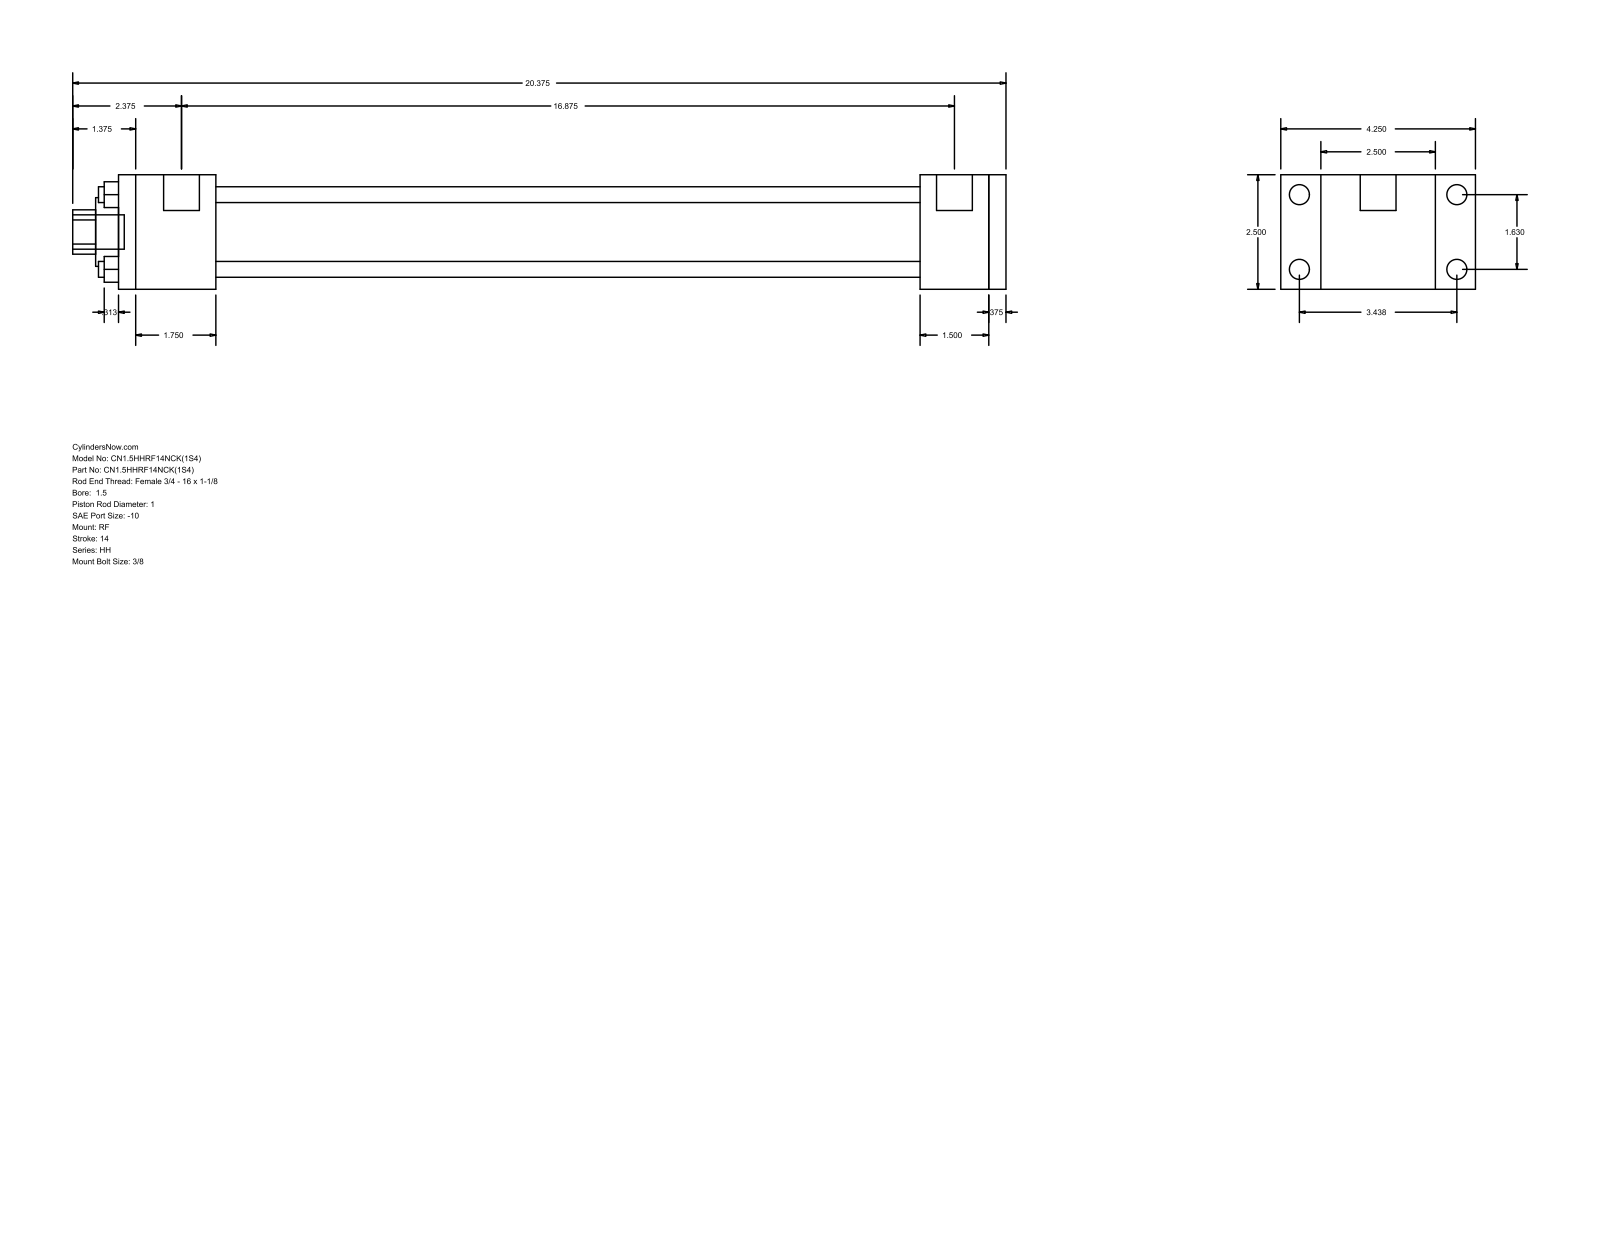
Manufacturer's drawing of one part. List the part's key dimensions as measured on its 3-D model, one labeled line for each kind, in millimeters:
Part name (STEP PRODUCT): HH_RF__0150_1
STEP written by: GSSL Pune (CONFIG_CONTROL_DESIGN)
Units: millimetres
Bodies: 0 solids, 92 faces (64 planar, 28 cylindrical, 0 other)
Overall size (bounding box): 517.52 × 107.95 × 63.5
Round holes (diameter × count): ⌀8.76 ×4, ⌀25.4 ×1, ⌀38.1 ×1, ⌀44.45 ×1
Round bosses / shafts (diameter × count): ⌀11.13 ×4, ⌀5.56 ×4, ⌀19.84 ×2, ⌀19.05 ×1
Partial cylindrical surfaces — rounded edges, fillets, slot ends (radius × count): R12.29 ×1
Main face-to-face distances: 63.5, 9.52, 390.52, 428.62, 438.14, 38.1, 47.62, 53.98, 444.5, 482.6
Hole centre spacings: 29.27, 41.4, 58.55
